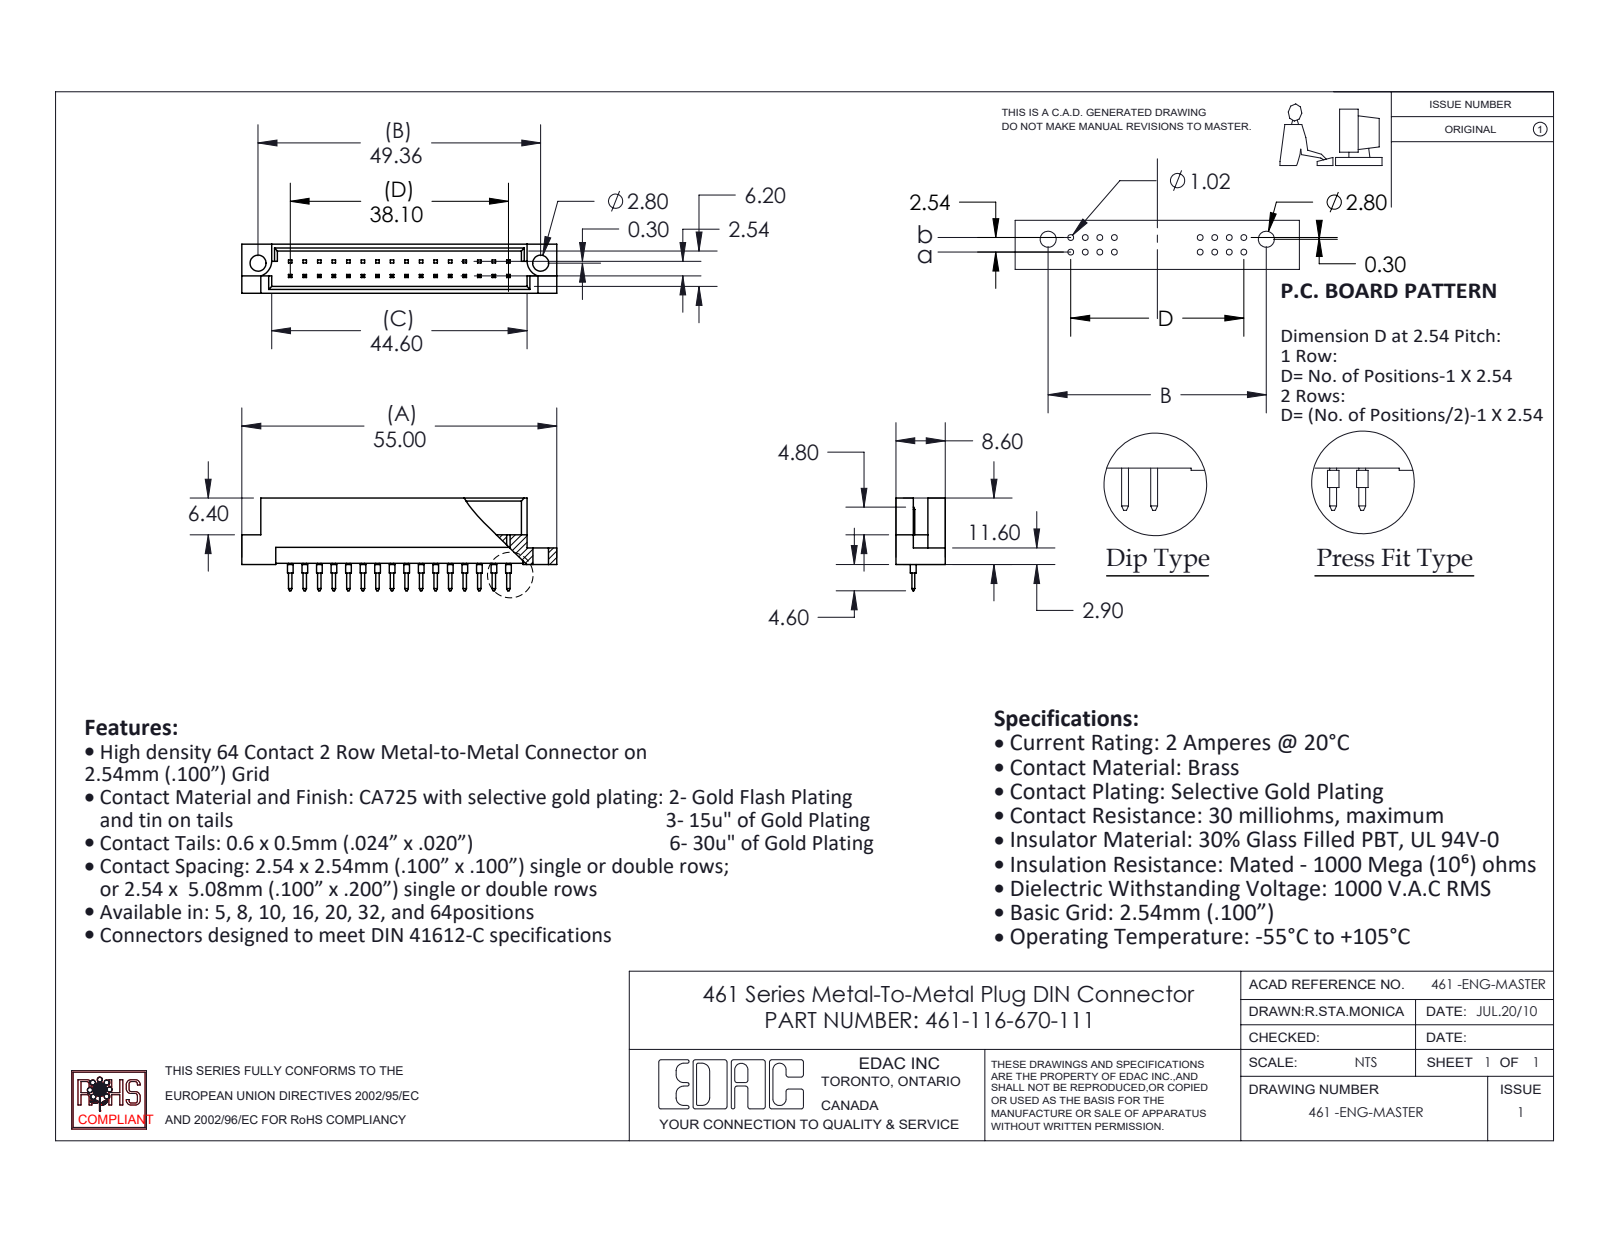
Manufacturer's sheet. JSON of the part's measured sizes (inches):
{"part_name": "461-290_70; 461 Part_32; 461-116-670-111", "step_written_by": "SolidWorks 2020 (CONFIG_CONTROL_DESIGN)", "units": "inches", "bodies": {"solids": 17, "faces": 528, "planar": 490, "cylindrical": 38, "other": 0}, "overall_size": [2.165, 0.638, 0.339], "volume_in3": 0.167, "surface_area_in2": 5.881, "round_holes": [[0.11, 2]], "round_bosses_or_shafts": [[0.039, 16]], "partial_cylinders_radius": [[0.11, 2]], "face_to_face_distances": [0.047, 0.291, 0.339, 0.244, 0.197, 0.1, 0.062, 0.109, 0.229, 0.182], "hole_center_spacings": [1.943]}
